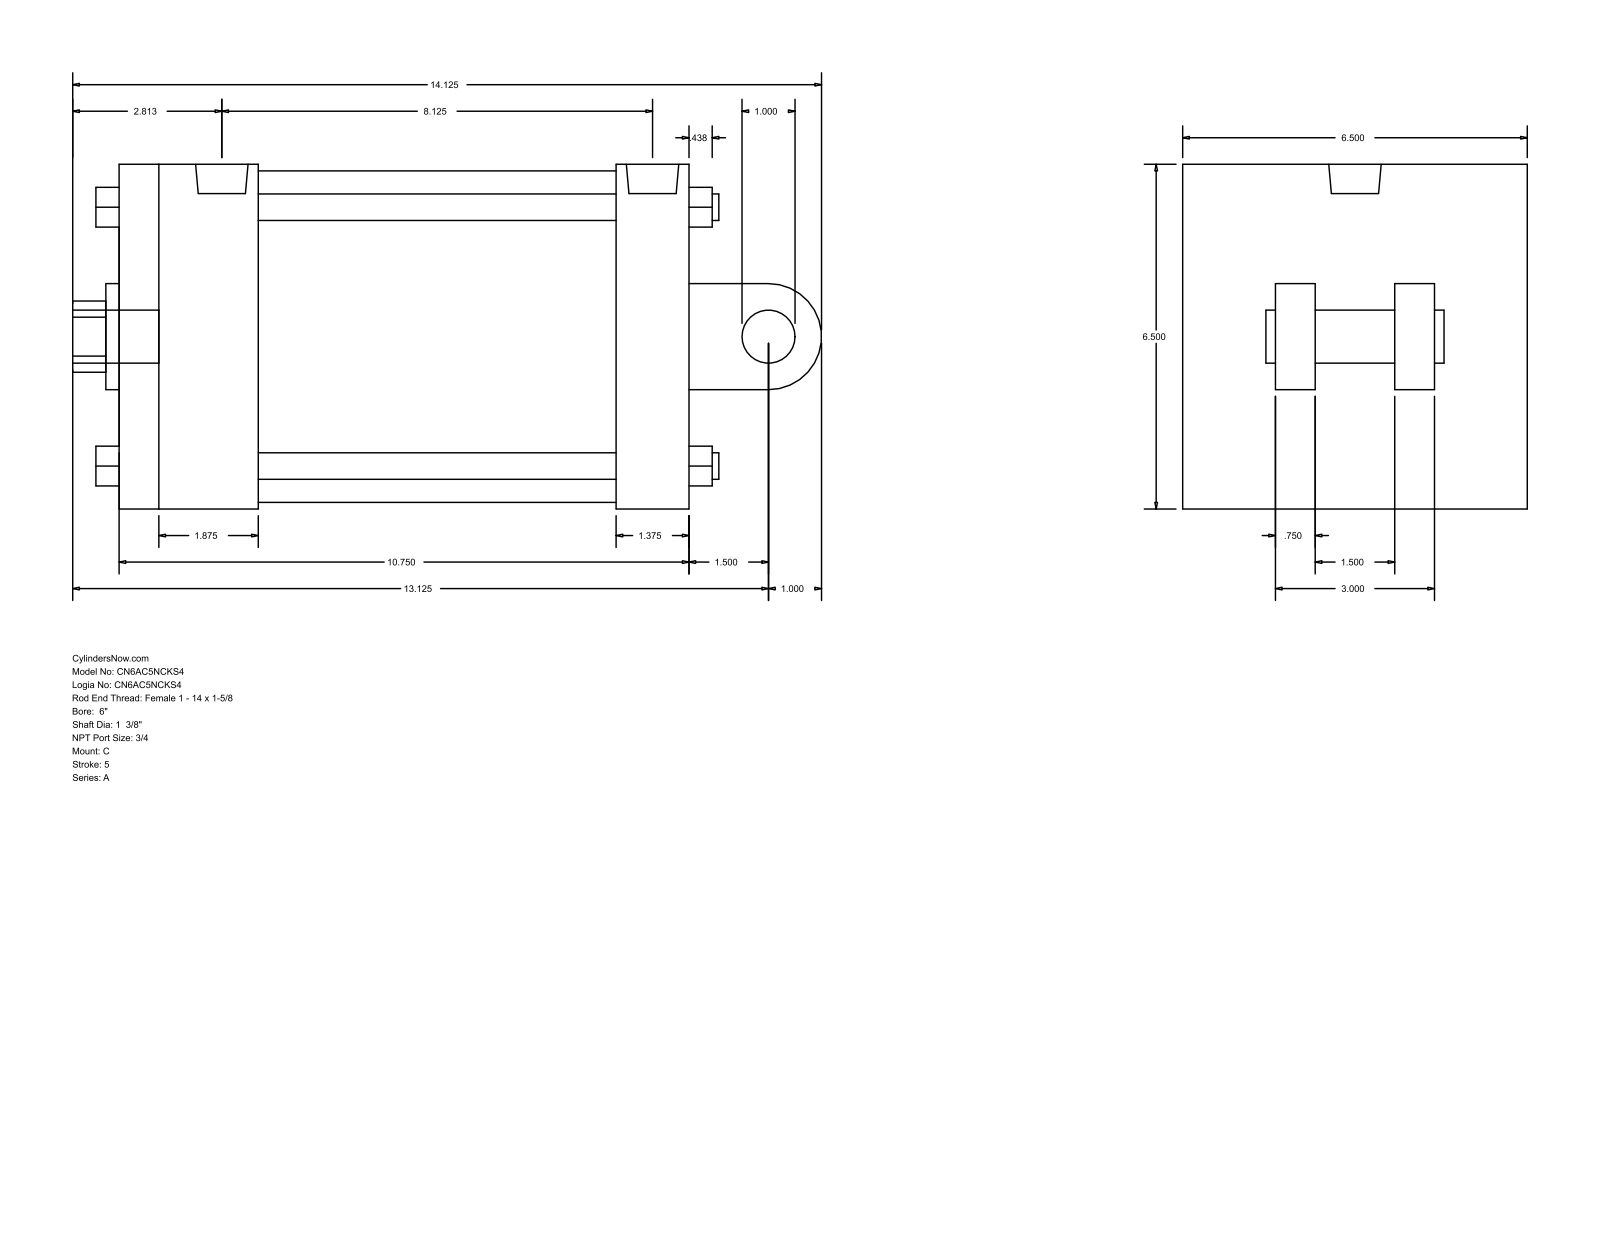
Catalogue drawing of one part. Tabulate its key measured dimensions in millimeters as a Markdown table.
| quantity | value |
| --- | --- |
| part name | A_C__0600_1.375 |
| STEP written by | GSSL Pune (CONFIG_CONTROL_DESIGN) |
| units | millimeters |
| bodies | 0 solids, 135 faces (102 planar, 33 cylindrical, 0 other) |
| overall size | 358.77 × 165.1 × 165.1 |
| round holes (diameter × count) | 15.08 × 2, 25.12 × 1, 34.92 × 1, 50.8 × 1, 158.75 × 1 |
| round bosses / shafts (diameter × count) | 12.7 × 4, 25.4 × 2, 15.08 × 2, 25.12 × 1 |
| partial cylindrical surfaces (radius × count) | 17.06 × 1, 25.4 × 1 |
| main face-to-face distances | 165.1, 273.04, 19.05, 57.15, 66.67, 206.37, 238.12, 171.45, 34.92, 44.45 |
| hole center spacings | 5.56 |
